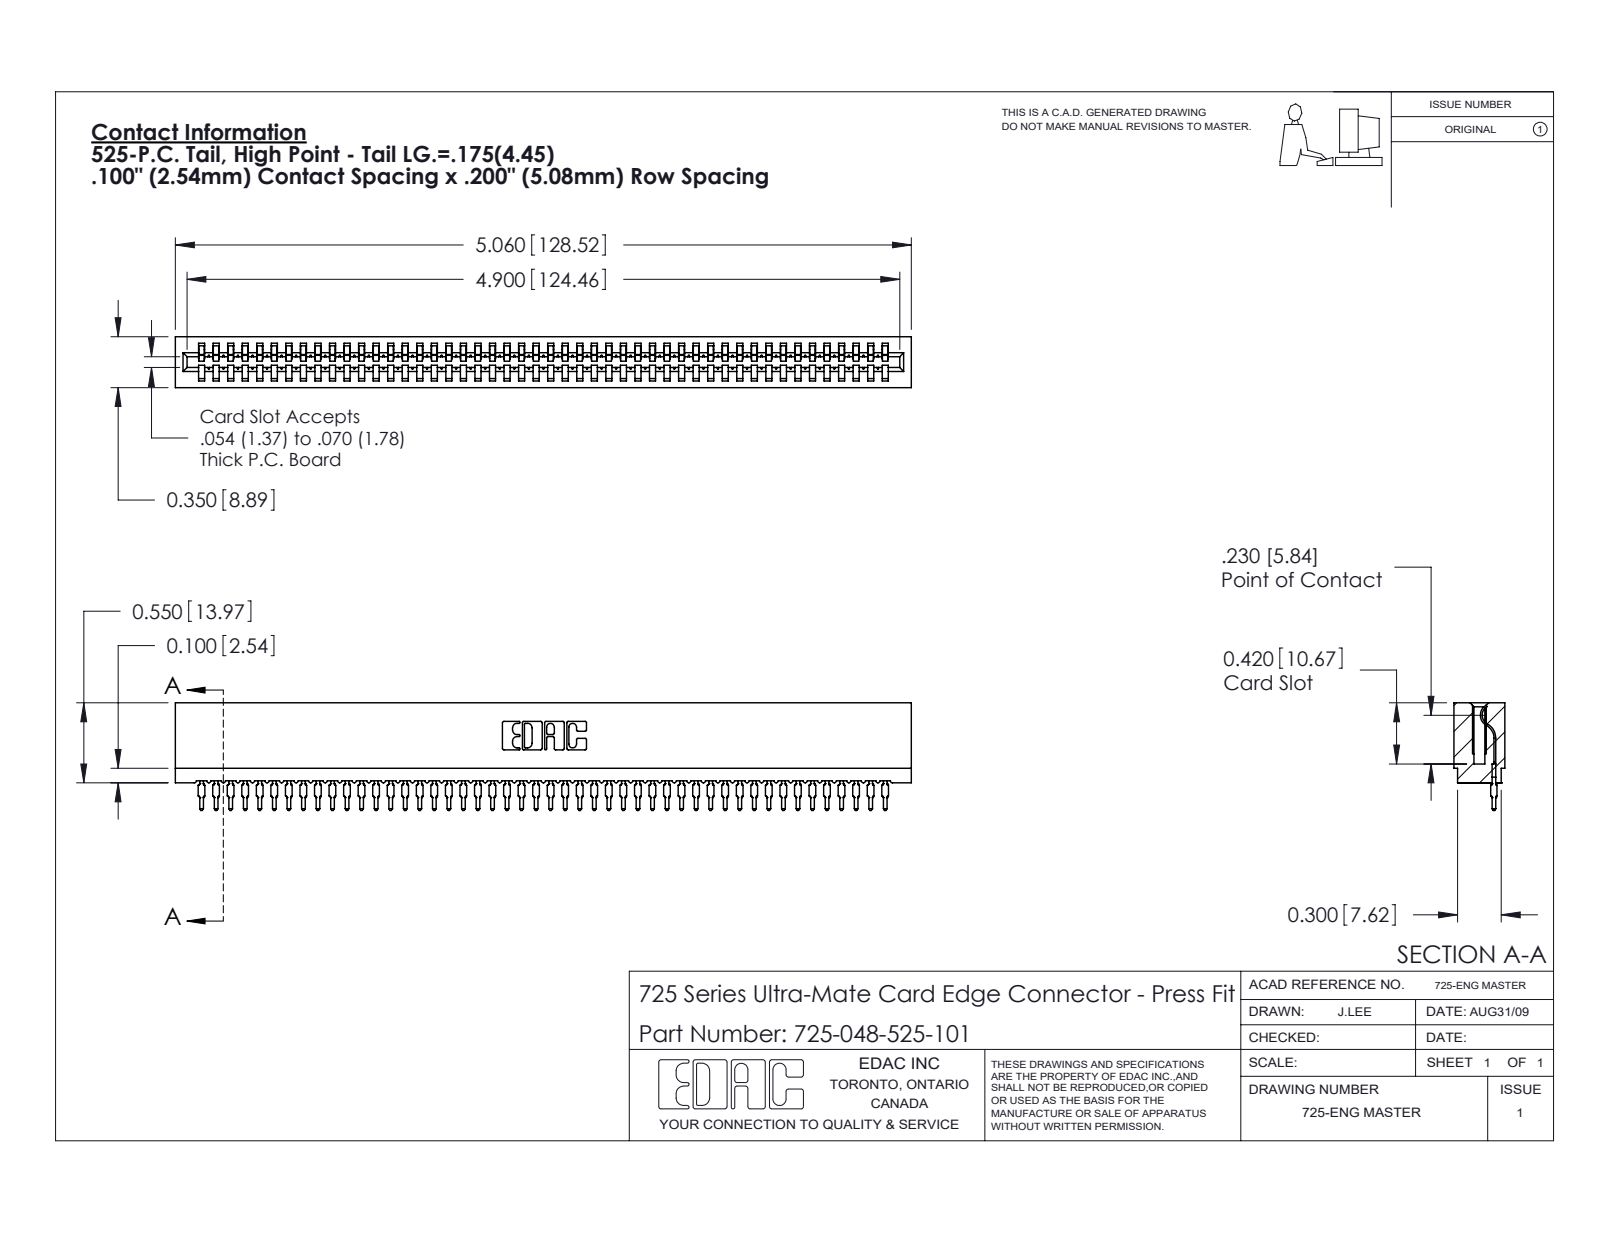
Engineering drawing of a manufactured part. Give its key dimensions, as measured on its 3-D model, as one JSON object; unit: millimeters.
{"part_name": "745-292-001_525; 725 Part_Insulator Option - 01; 725-048-525-101", "step_written_by": "SolidWorks 2020 (CONFIG_CONTROL_DESIGN)", "units": "millimeters", "bodies": {"solids": 49, "faces": 5471, "planar": 3271, "cylindrical": 952, "other": 1248}, "overall_size": [128.5, 18.8, 8.9], "volume_mm3": 9680, "surface_area_mm2": 18650, "partial_cylinders_radius": [[0.4, 96], [0.5, 96], [0.3, 22], [0.2, 6], [0.8, 6], [0.1, 4], [0.3, 4], [0.7, 3]], "face_to_face_distances": [8.9, 5.1, 5.4, 3.5, 1.1, 7.7, 2.4, 4.2, 2.5, 1.6]}
